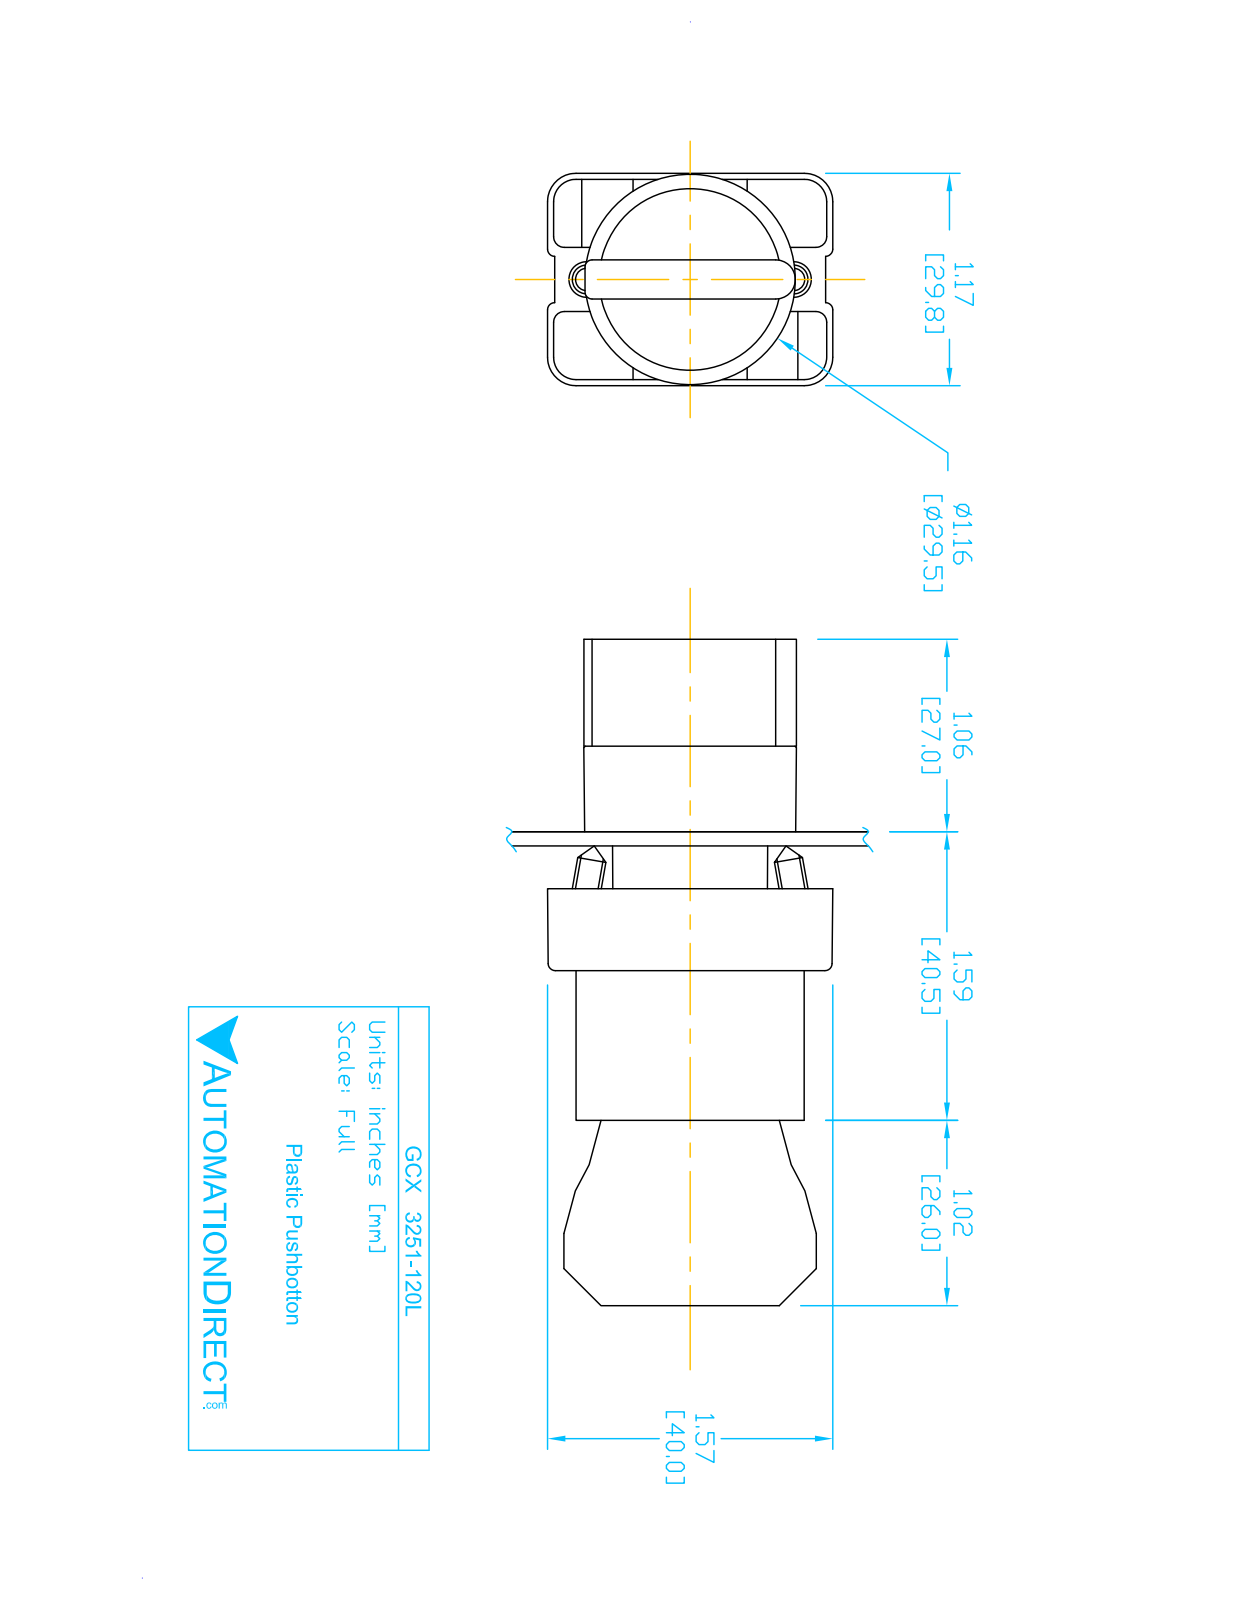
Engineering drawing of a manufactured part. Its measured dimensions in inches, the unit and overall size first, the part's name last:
Units: inches
Overall size (bounding box): 3.653 × 1.581 × 1.177
Round holes (diameter × count): ⌀0.079 ×2, ⌀0.124 ×2, ⌀0.13 ×2, ⌀0.087 ×1, ⌀0.197 ×1, ⌀0.469 ×1, ⌀0.878 ×1, ⌀0.888 ×1, ⌀1.024 ×1
Round bosses / shafts (diameter × count): ⌀0.157 ×4, ⌀1.175 ×1, ⌀1.004 ×1, ⌀0.945 ×1, ⌀0.856 ×1, ⌀0.78 ×1, ⌀0.504 ×1
Partial cylindrical surfaces — rounded edges, fillets, slot ends (radius × count): R0.059 ×24, R0.041 ×12, R0.124 ×12, R0.157 ×12, R0.039 ×9, R0.128 ×2, R0.02 ×1, R0.063 ×1
Main face-to-face distances: 0.827, 2.02, 1.193, 0.579, 1.244, 1.171, 0.472, 0.469, 0.031, 0.033
Hole centre spacings: 0.236, 0.544, 0.472, 0.49
Volume: 2.799 in³ · Surface area: 39 in²
Bodies: 8 solids, 445 faces (263 planar, 151 cylindrical, 31 other)
Part name (STEP PRODUCT): GCX3251L OPERATOR; ECX3029-2; ECX1050; ecx1040 (+1 more)
STEP written by: SolidWorks 2016 (AUTOMOTIVE_DESIGN)
